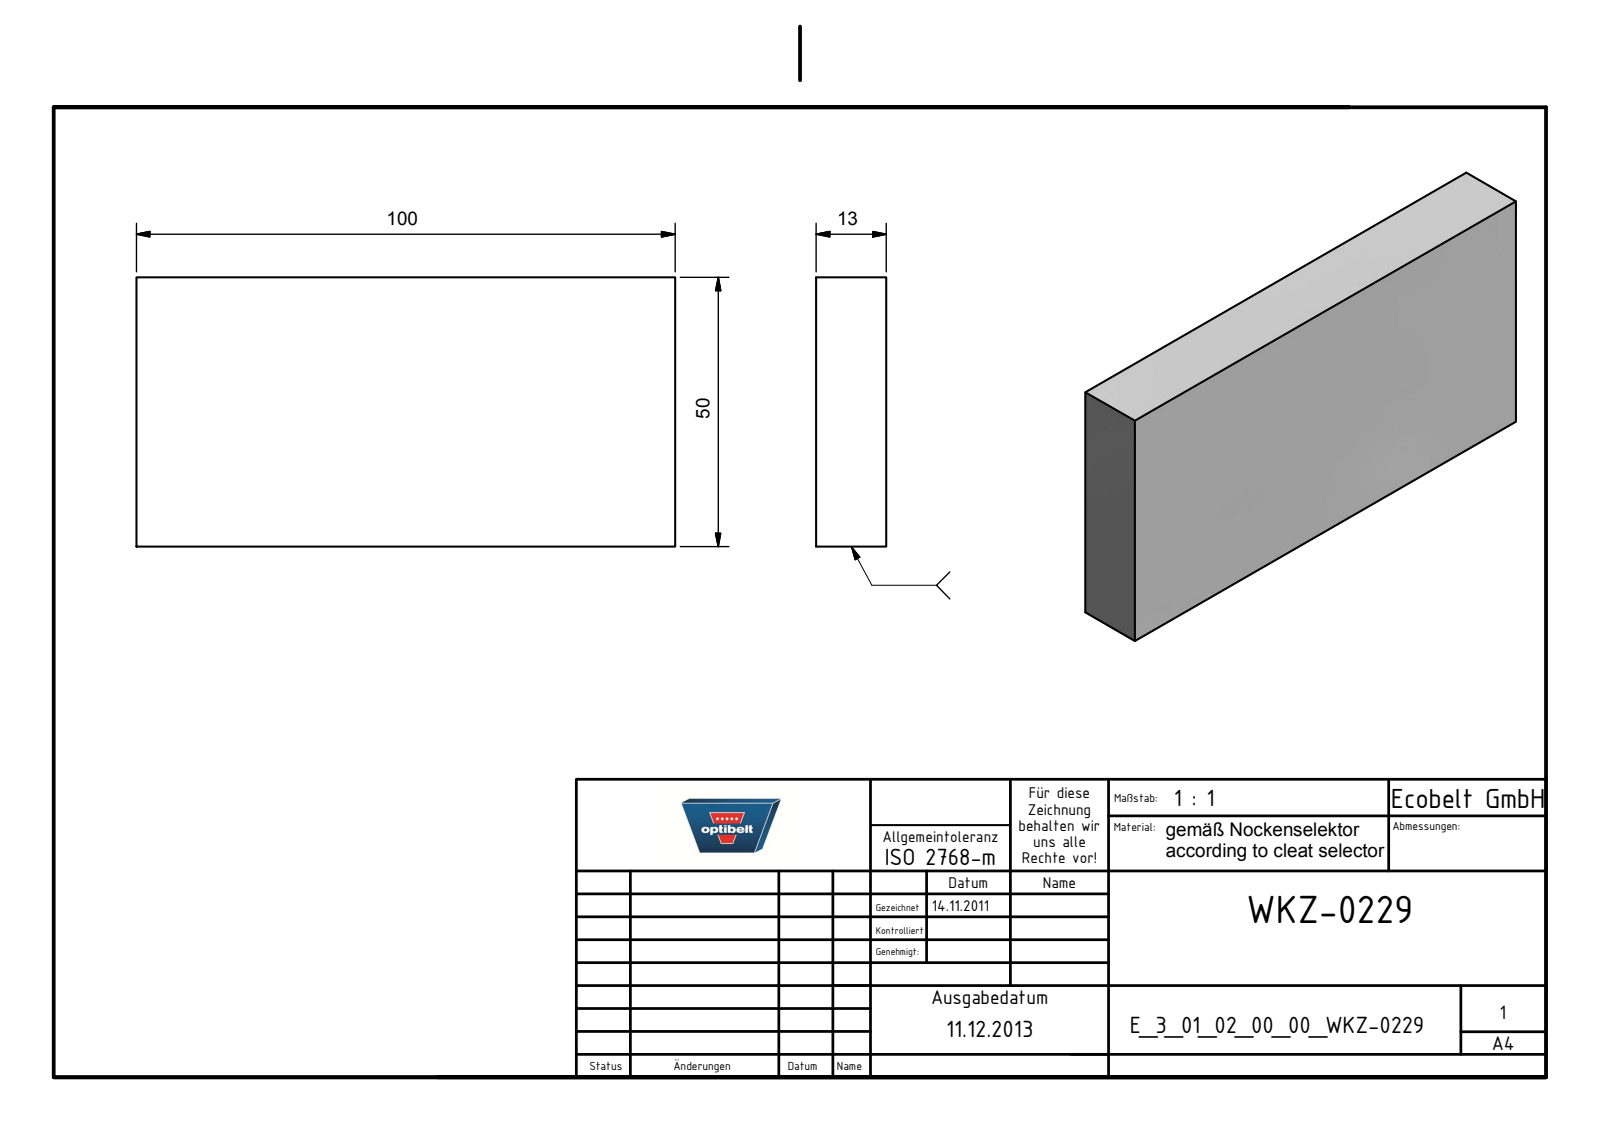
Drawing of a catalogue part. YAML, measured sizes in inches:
part_name: "E_3_01_02_00_00_WKZ-0229"
step_written_by: "Autodesk Inventor 2021 (AUTOMOTIVE_DESIGN)"
units: inches
bodies: {solids: 1, faces: 6, planar: 6, cylindrical: 0, other: 0}
overall_size: [3.937, 1.969, 0.512]
volume: 3.967
surface_area: 21.55
face_to_face_distances: [0.512, 1.969, 3.937]
